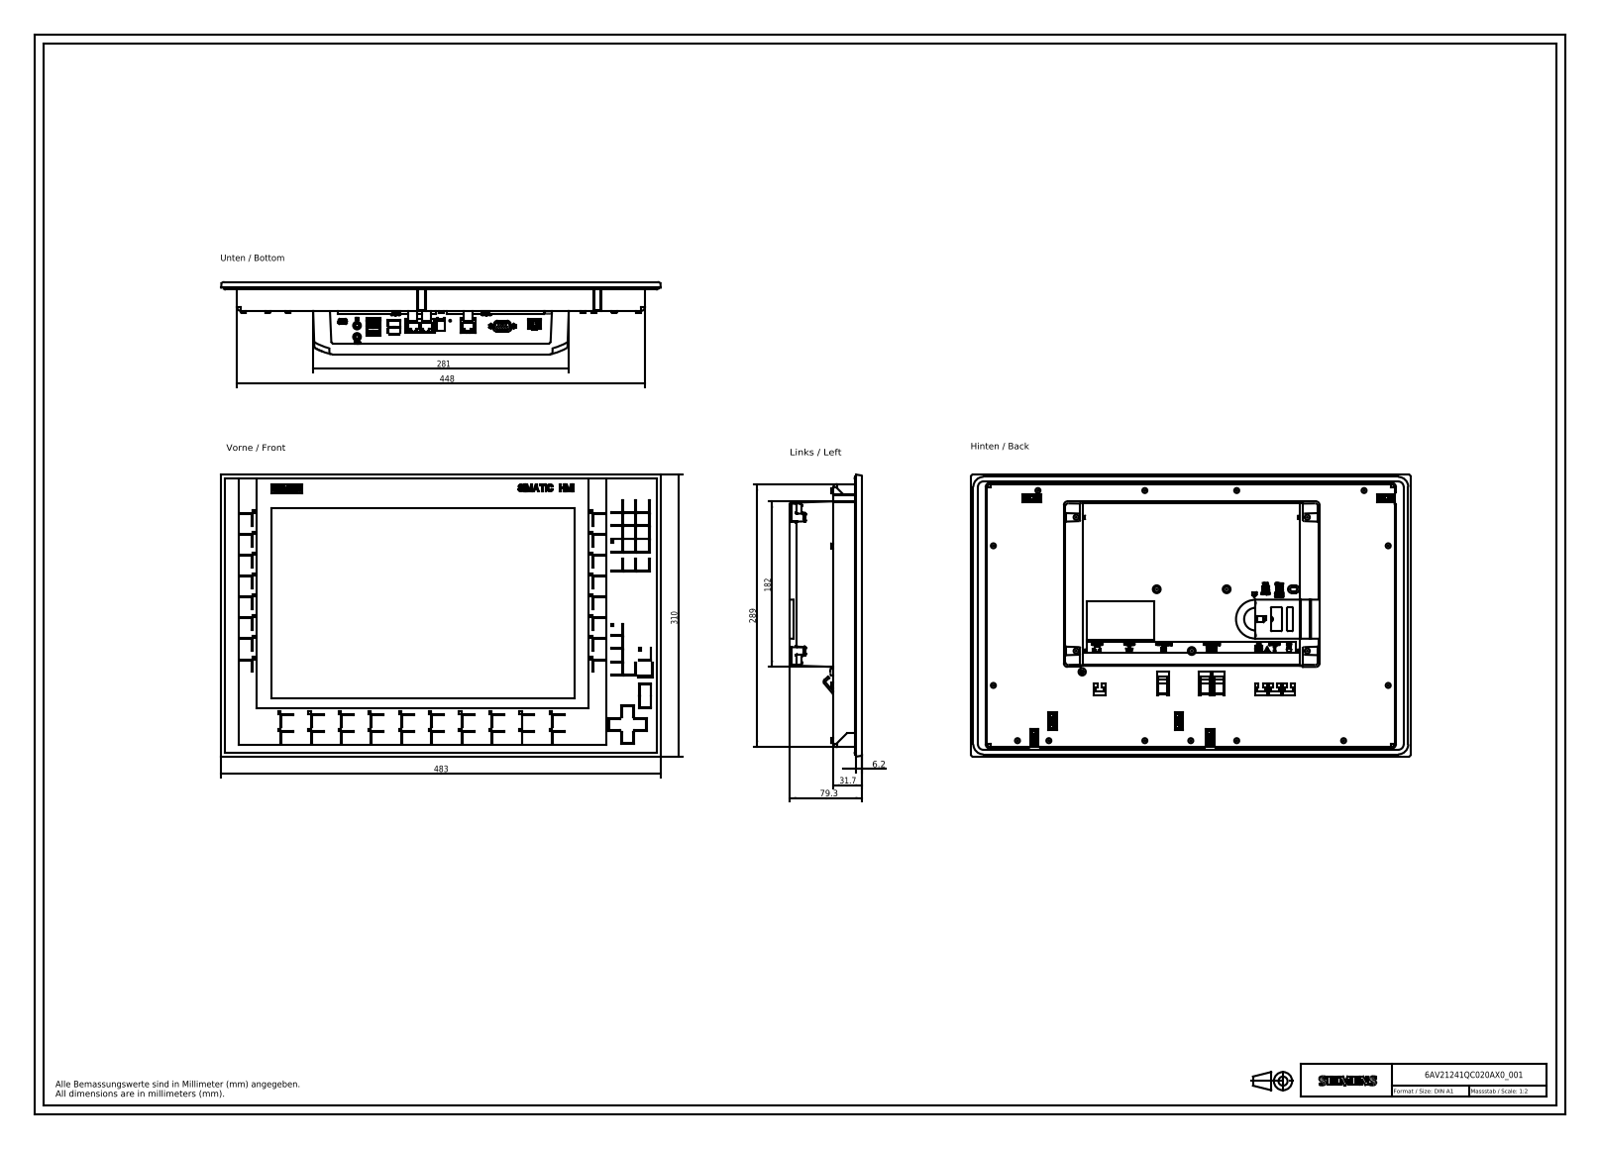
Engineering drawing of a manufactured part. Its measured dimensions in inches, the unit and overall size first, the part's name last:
Units: inches
Overall size (bounding box): 19.016 × 12.205 × 3.126
Round holes (diameter × count): ⌀0.031 ×9, ⌀0.316 ×3, ⌀0.071 ×2, ⌀0.094 ×2, ⌀0.112 ×2, ⌀0.15 ×2, ⌀0.335 ×2
Round bosses / shafts (diameter × count): ⌀0.236 ×8, ⌀0.276 ×2, ⌀0.12 ×2, ⌀0.118 ×2, ⌀0.079 ×2, ⌀0.315 ×1
Partial cylindrical surfaces — rounded edges, fillets, slot ends (radius × count): R0.033 ×48, R0.05 ×8, R0.039 ×4, R0.073 ×4, R0.156 ×4, R0.235 ×4, R0.236 ×4, R0.414 ×4
Main face-to-face distances: 1.213, 1.587, 0.374, 0.335, 0.039, 1.547, 1.5, 1.539, 1.874, 3.087
Hole centre spacings: 0.114, 0.108, 0.19, 0.216, 0.288, 0.324, 0.391, 0.492
Volume: 395.9 in³ · Surface area: 858.8 in²
Bodies: 344 solids, 3561 faces (3100 planar, 220 cylindrical, 241 other)
Part name (STEP PRODUCT): A5E30321192A_001; A5E30986546A_001; A5E30986540A_001; A5E30986534A_001 (+1 more)
STEP written by: SIEMENS PLM Software NX 7.5 (AUTOMOTIVE_DESIGN)
